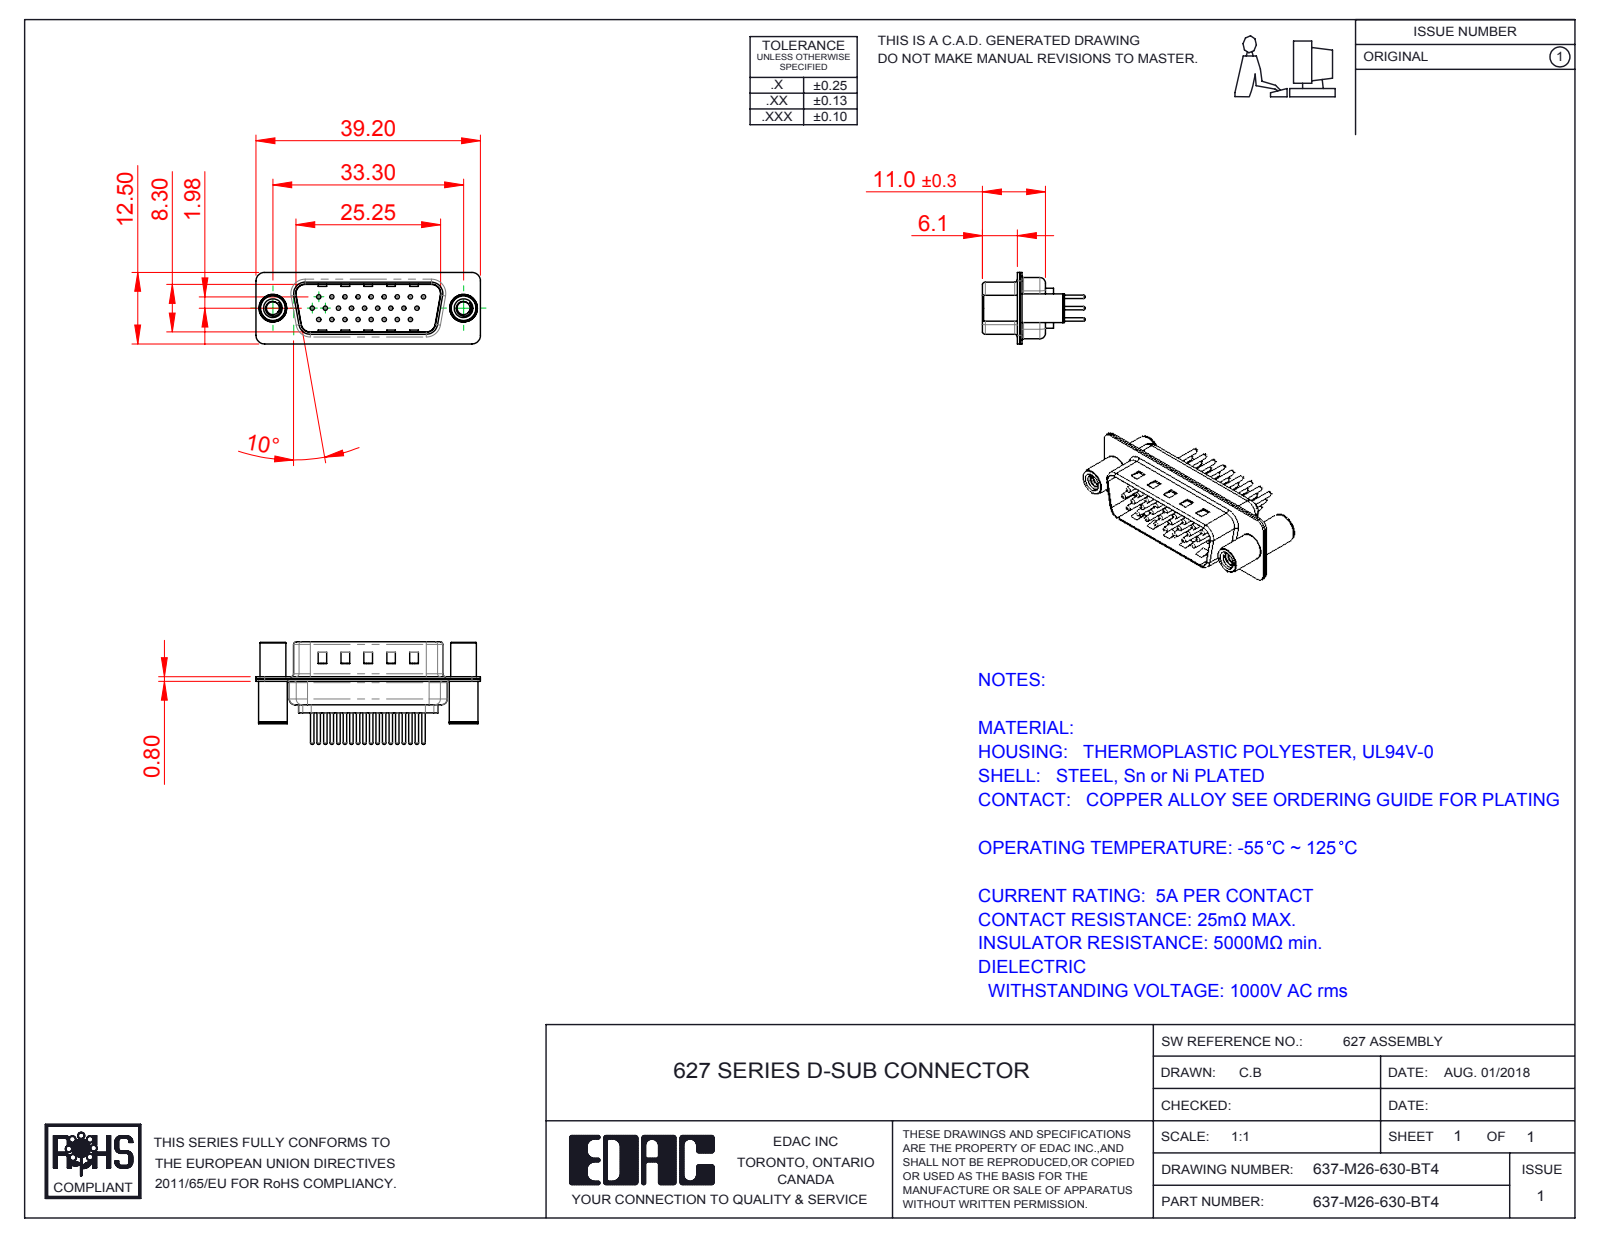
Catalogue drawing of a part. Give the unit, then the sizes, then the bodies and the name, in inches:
Units: inches
Overall size (bounding box): 1.543 × 0.705 × 0.492
Round holes (diameter × count): ⌀0.03 ×26, ⌀0.063 ×26, ⌀0.079 ×26, ⌀0.089 ×2, ⌀0.128 ×2, ⌀0.157 ×2, ⌀0.189 ×2
Round bosses / shafts (diameter × count): ⌀0.059 ×26, ⌀0.024 ×26, ⌀0.197 ×2, ⌀0.193 ×2, ⌀0.177 ×2
Partial cylindrical surfaces — rounded edges, fillets, slot ends (radius × count): R0.059 ×16, R0.079 ×12, R0.02 ×8, R0.063 ×8, R0.01 ×4, R0.024 ×4, R0.026 ×4, R0.035 ×4
Main face-to-face distances: 0.016, 0.031, 0.374, 0.358, 0.343, 0.39, 0.248, 0.03, 0.217, 0.014
Hole centre spacings: 0.156, 0.09, 0.18, 0.238, 0.09, 0.324, 0.27, 0.413
Volume: 0.134 in³ · Surface area: 9.734 in²
Bodies: 31 solids, 1388 faces (327 planar, 549 cylindrical, 512 other)
Part name (STEP PRODUCT): 637M Shell Front_26 Contacts; 637-M26-630-BT4; 637M Housing_26 Contacts; 637M Contact Row 3_30 (+4 more)
STEP written by: SolidWorks 2016 (CONFIG_CONTROL_DESIGN)
